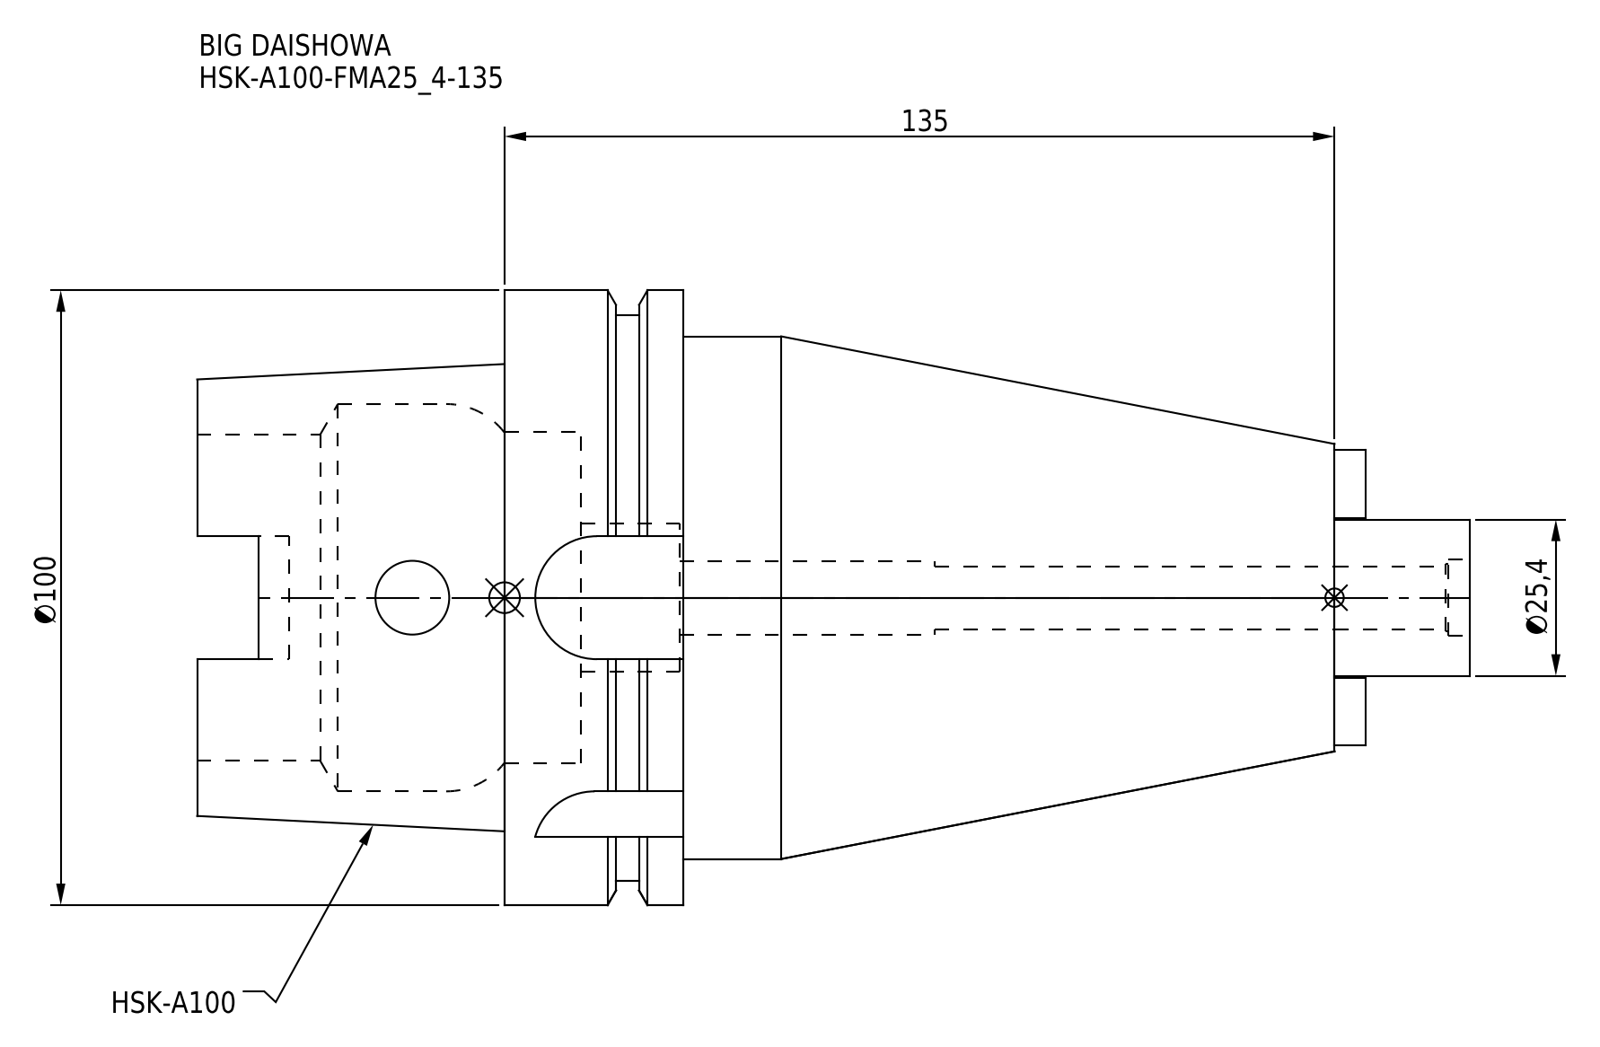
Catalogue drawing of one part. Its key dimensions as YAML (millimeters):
part_name: "HSK-A100-FMA25_4-135"
step_written_by: "CREO PARAMETRIC BY PTC INC, 2016380 (AUTOMOTIVE_DESIGN)"
units: millimeters
bodies: {solids: 1, faces: 106, planar: 46, cylindrical: 44, other: 16}
overall_size: [207, 100, 100]
volume: 673734
surface_area: 76392
round_holes:
  - {diameter: 12, count: 2}
  - {diameter: 10.25, count: 1}
  - {diameter: 11, count: 1}
  - {diameter: 12.5, count: 1}
  - {diameter: 24, count: 1}
  - {diameter: 53, count: 1}
  - {diameter: 53.8, count: 1}
  - {diameter: 63, count: 1}
round_bosses_or_shafts:
  - {diameter: 100, count: 1}
  - {diameter: 92, count: 1}
  - {diameter: 85, count: 1}
  - {diameter: 25.4, count: 1}
partial_cylinders:
  - {radius: 4.88, count: 4}
  - {radius: 10, count: 4}
face_to_face_distances: [29, 16.55, 12.45, 135, 106, 122.55, 185, 79, 62.45, 50]
